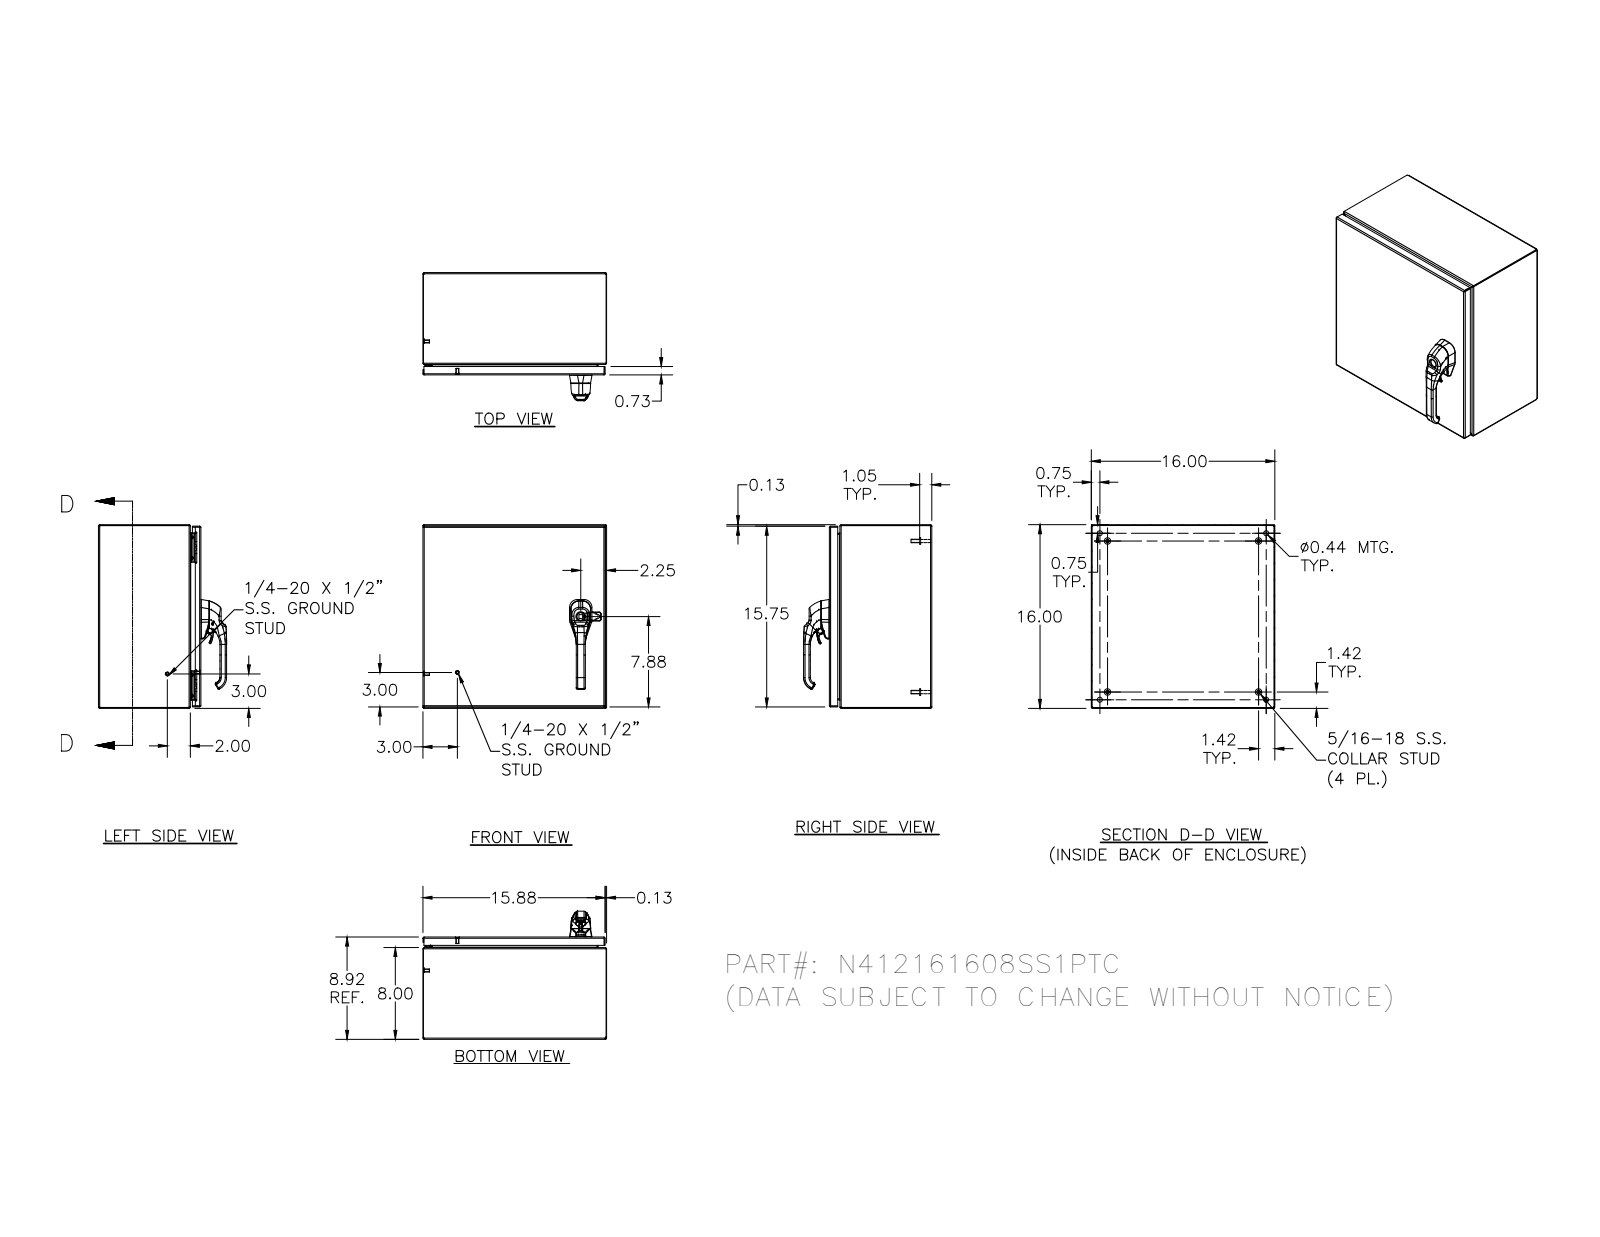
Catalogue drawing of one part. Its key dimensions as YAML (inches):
part_name: "N412161608SS1PTC; NA12161608SS1PTCBKP; N4121616SS1PTCLID; HFW328176 (+8 more)"
step_written_by: "Autodesk Inventor 2012 (AUTOMOTIVE_DESIGN)"
units: inches
bodies: {solids: 41, faces: 2782, planar: 882, cylindrical: 1035, other: 865}
overall_size: [16, 16, 11.166]
volume: 92.7
surface_area: 2423
round_holes:
  - {diameter: 0.093, count: 4}
  - {diameter: 0.152, count: 4}
  - {diameter: 0.167, count: 4}
  - {diameter: 0.172, count: 4}
  - {diameter: 0.188, count: 4}
  - {diameter: 0.437, count: 4}
  - {diameter: 0.213, count: 3}
  - {diameter: 0.281, count: 3}
  - {diameter: 0.156, count: 2}
  - {diameter: 0.315, count: 2}
  - {diameter: 0.402, count: 2}
  - {diameter: 0.413, count: 2}
round_bosses_or_shafts:
  - {diameter: 0.25, count: 10}
  - {diameter: 0.563, count: 4}
  - {diameter: 0.36, count: 4}
  - {diameter: 0.32, count: 4}
  - {diameter: 0.3, count: 4}
  - {diameter: 0.275, count: 4}
  - {diameter: 0.256, count: 4}
  - {diameter: 0.164, count: 4}
partial_cylinders:
  - {radius: 0.02, count: 173}
  - {radius: 0.012, count: 101}
  - {radius: 0.031, count: 30}
  - {radius: 0.05, count: 26}
  - {radius: 0.019, count: 21}
  - {radius: 0.105, count: 20}
  - {radius: 0.016, count: 18}
  - {radius: 0.079, count: 14}
face_to_face_distances: [0.074, 15.926, 8.843, 15.852, 16, 8.917, 8.769, 7.926, 0.917, 0.125]
hole_center_spacings: [11.996, 14.5, 0.017, 0.66, 12.656, 14.181, 15.173, 0.019]
